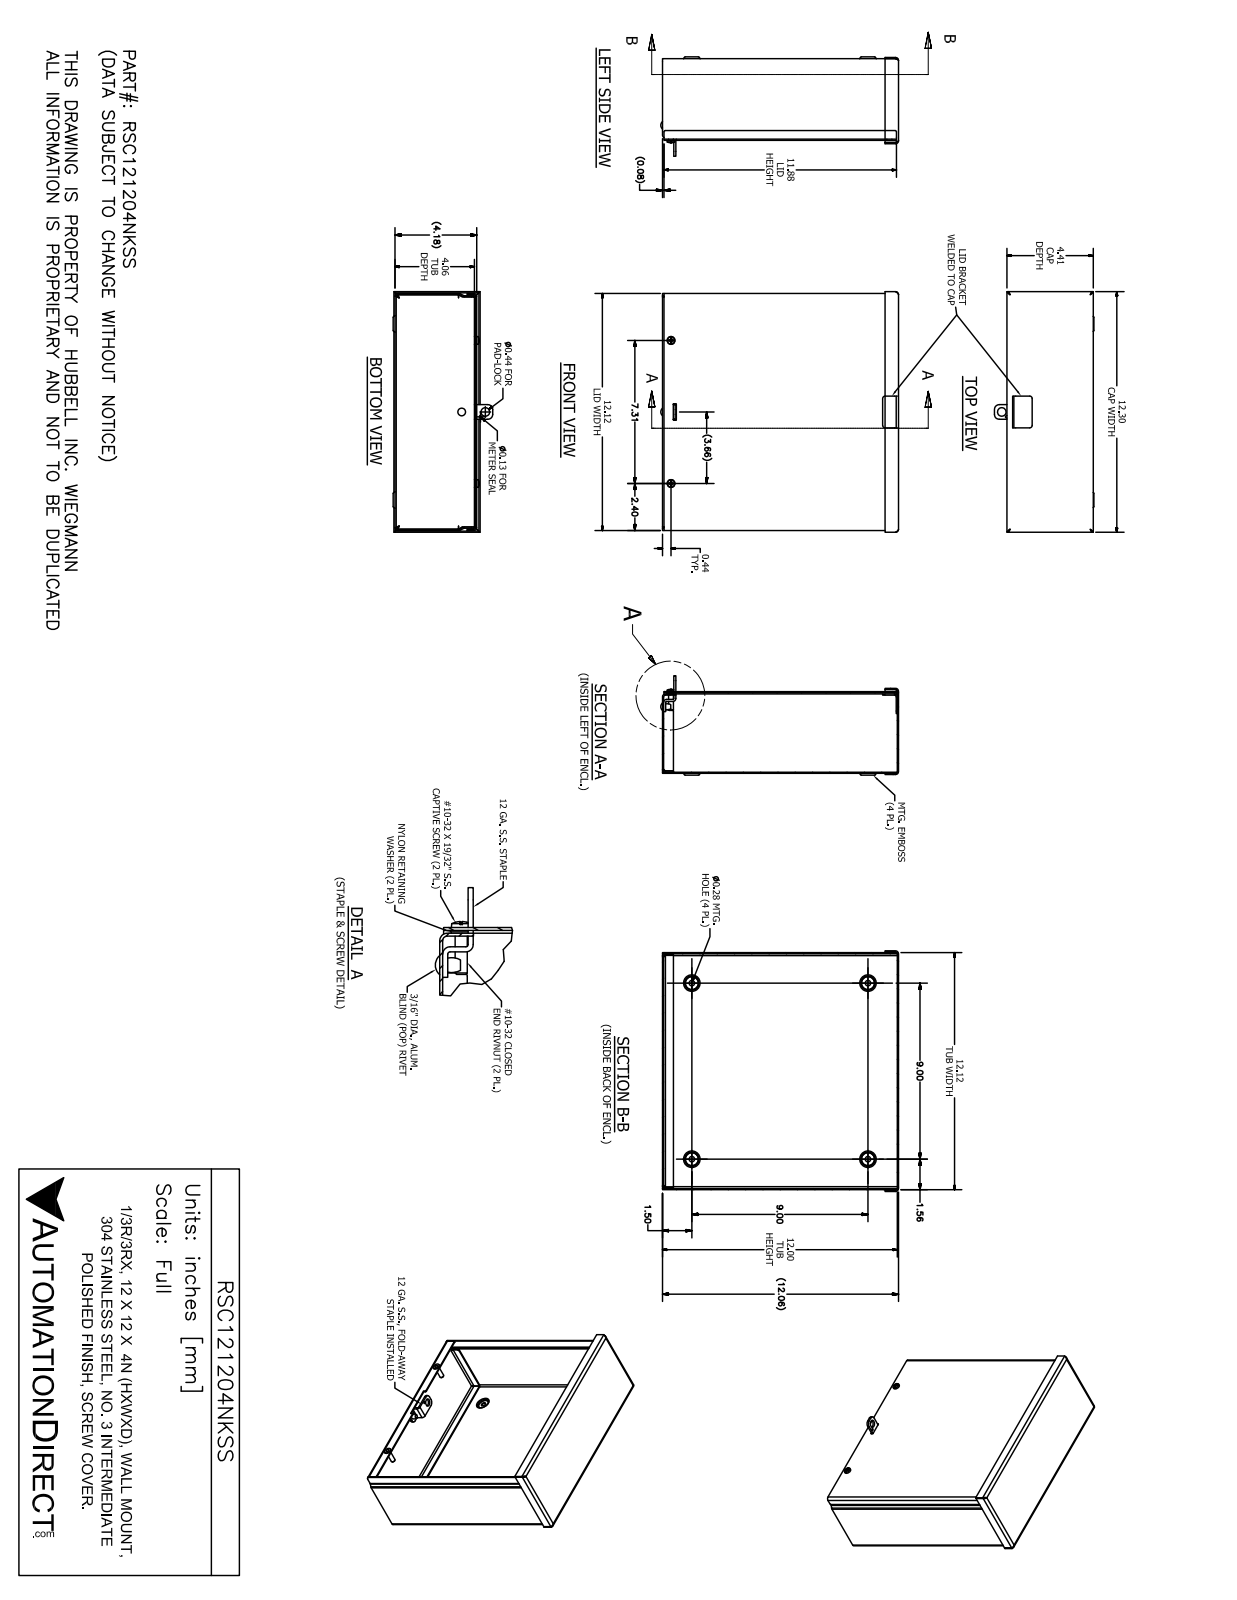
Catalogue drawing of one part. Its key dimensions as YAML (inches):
part_name: "RSC121204NKSS"
step_written_by: "SolidWorks 2017 (AUTOMOTIVE_DESIGN)"
units: inches
bodies: {solids: 13, faces: 383, planar: 199, cylindrical: 99, other: 85}
overall_size: [12.299, 12.149, 5.084]
volume: 31.67
surface_area: 1085
round_holes:
  - {diameter: 0.25, count: 4}
  - {diameter: 0.281, count: 4}
  - {diameter: 0.156, count: 2}
  - {diameter: 0.196, count: 2}
  - {diameter: 0.257, count: 2}
  - {diameter: 0.278, count: 2}
  - {diameter: 0.125, count: 1}
  - {diameter: 0.198, count: 1}
  - {diameter: 0.201, count: 1}
  - {diameter: 0.437, count: 1}
round_bosses_or_shafts:
  - {diameter: 0.453, count: 2}
  - {diameter: 0.406, count: 2}
  - {diameter: 0.248, count: 2}
  - {diameter: 0.167, count: 2}
  - {diameter: 0.187, count: 1}
partial_cylinders:
  - {radius: 0.094, count: 17}
  - {radius: 0.153, count: 17}
  - {radius: 0.031, count: 6}
  - {radius: 0.125, count: 4}
  - {radius: 0.25, count: 4}
  - {radius: 0.062, count: 3}
  - {radius: 0.047, count: 2}
  - {radius: 0.05, count: 2}
face_to_face_distances: [0.059, 4.117, 4.176, 4.058, 12, 12.059, 11.941, 12.118, 0.059, 0.117]
hole_center_spacings: [9, 1.357, 1.381, 7.313, 8.225, 8.229, 10.098, 10.129]
